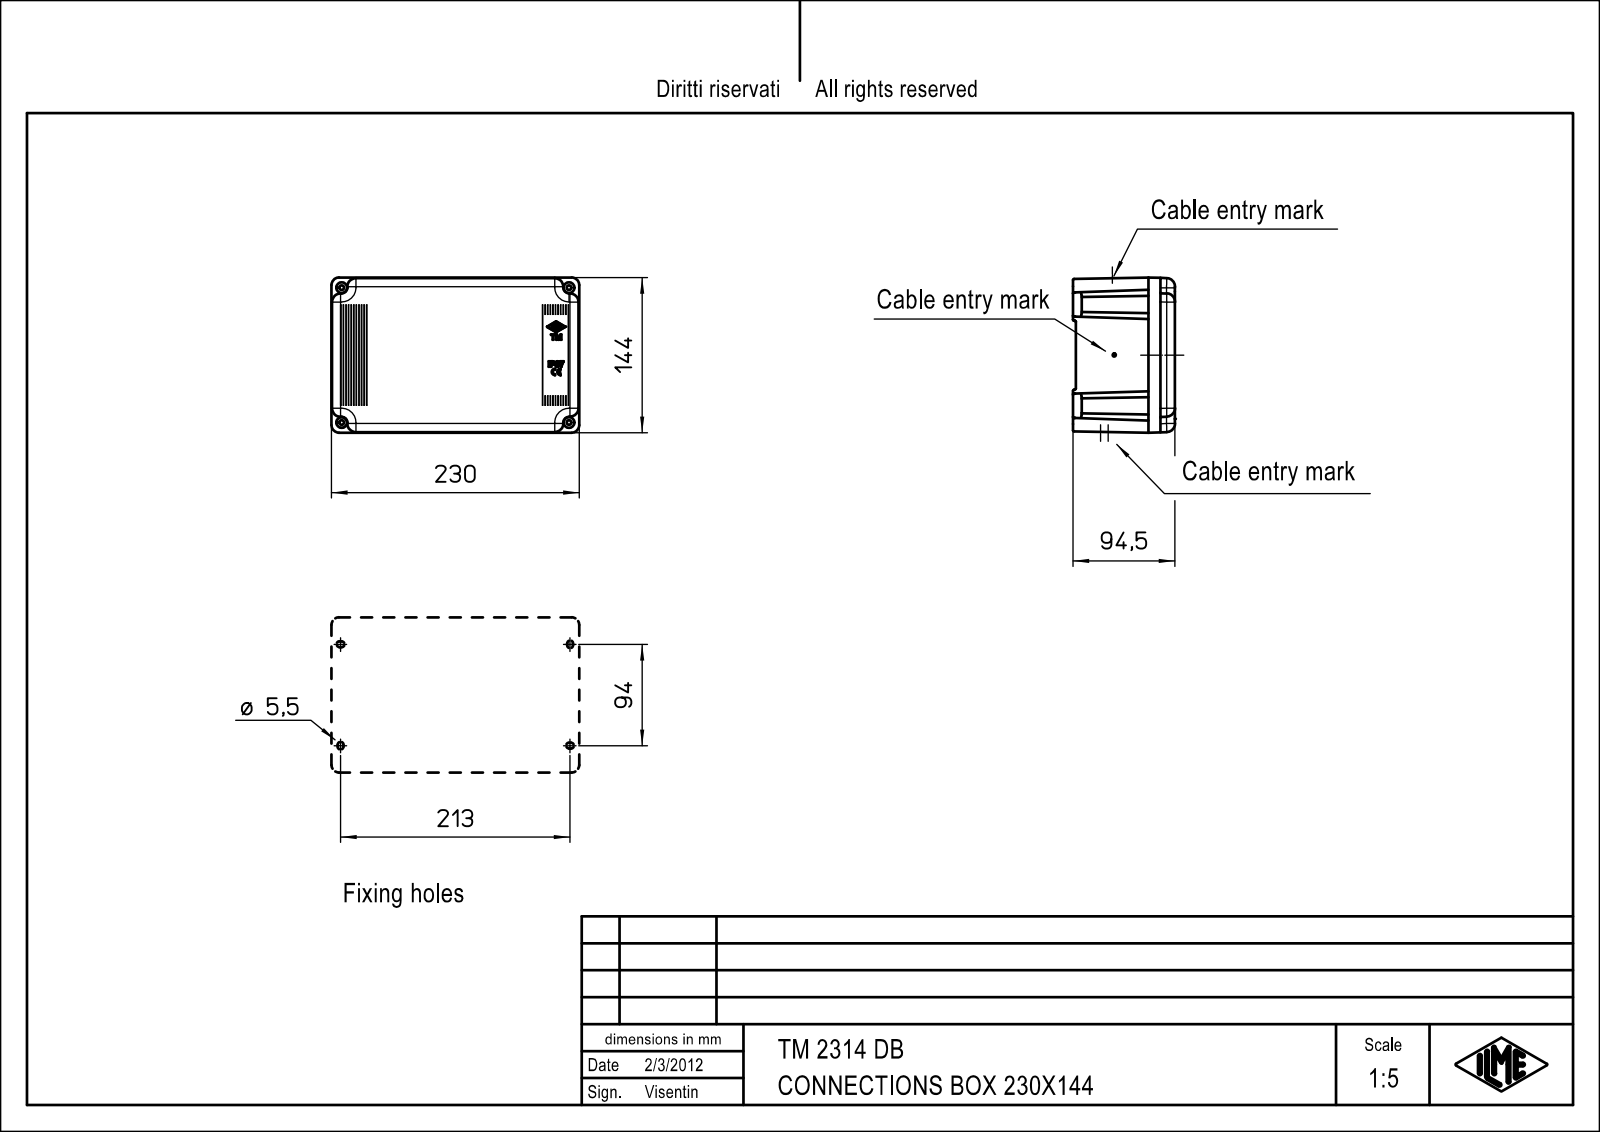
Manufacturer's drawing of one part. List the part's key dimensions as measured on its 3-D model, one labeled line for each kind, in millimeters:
Part name (STEP PRODUCT): COPERCHIO_2314; SCATOLA_2314; TM_2314_DB
STEP written by: Creo Elements/Direct Modeling 20.5B 27-May-2023 (C) Parametric Technology GmbH (AUTOMOTIVE_DESIGN)
Units: millimetres
Bodies: 2 solids, 1161 faces (820 planar, 257 cylindrical, 84 other)
Overall size (bounding box): 230 × 144 × 94.9
Volume: 726 582 mm³ · Surface area: 271 247 mm²
Round holes (diameter × count): ⌀5.2 ×4, ⌀10.26 ×4
Round bosses / shafts (diameter × count): ⌀8.5 ×4, ⌀5 ×4
Partial cylindrical surfaces — rounded edges, fillets, slot ends (radius × count): R0.2 ×124, R3.5 ×16, R8 ×16, R0.25 ×11, R2.7 ×8, R3 ×8, R7 ×8, R9.5 ×8
Main face-to-face distances: 87, 5, 92, 82, 5.37, 62.5, 24.5, 67.5, 19.5, 7.51
Hole centre spacings: 125, 211, 245.25
